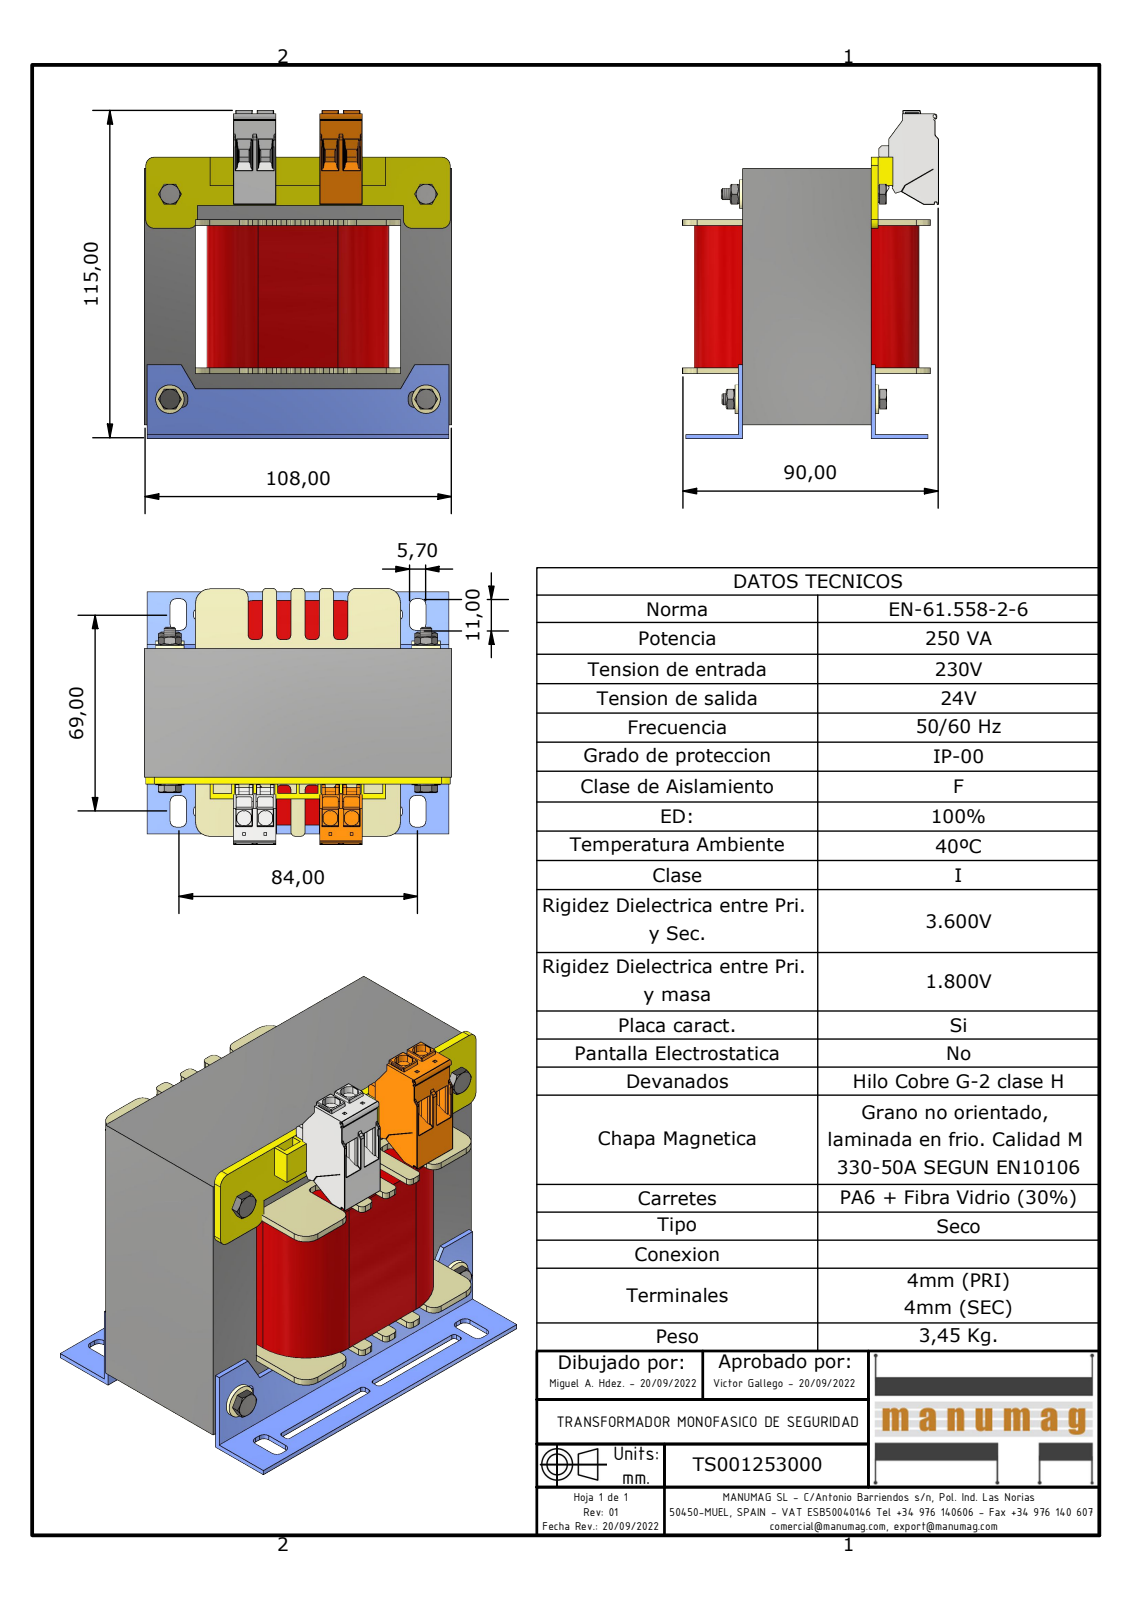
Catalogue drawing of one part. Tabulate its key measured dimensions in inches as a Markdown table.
| quantity | value |
| --- | --- |
| part name | TS001253000; EI108 x 90 - 45 (RC36); AF36DIN; centrador M4 (+6 more) |
| STEP written by | Autodesk Inventor 2023 (AUTOMOTIVE_DESIGN) |
| units | inches |
| bodies | 21 solids, 3789 faces (3021 planar, 528 cylindrical, 240 other) |
| overall size | 4.542 × 4.252 × 3.539 |
| volume | 33.51 in³ |
| surface area | 193 in² |
| round holes (diameter × count) | 0.128 × 4, 0.157 × 4, 0.22 × 4 |
| round bosses / shafts (diameter × count) | 0.394 × 4, 0.232 × 4, 0.193 × 4, 0.143 × 4 |
| partial cylindrical surfaces (radius × count) | 0.006 × 160, 0.008 × 48, 0.059 × 28, 0.079 × 24, 0.039 × 20, 0.02 × 12, 0.118 × 10, 0.197 × 8 |
| main face-to-face distances | 0.709, 2.835, 1.417, 1.772, 2.126, 3.543, 0.059, 1.969, 0.157, 0.866 |
| hole center spacings | 2.835, 3.543, 4.538 |
